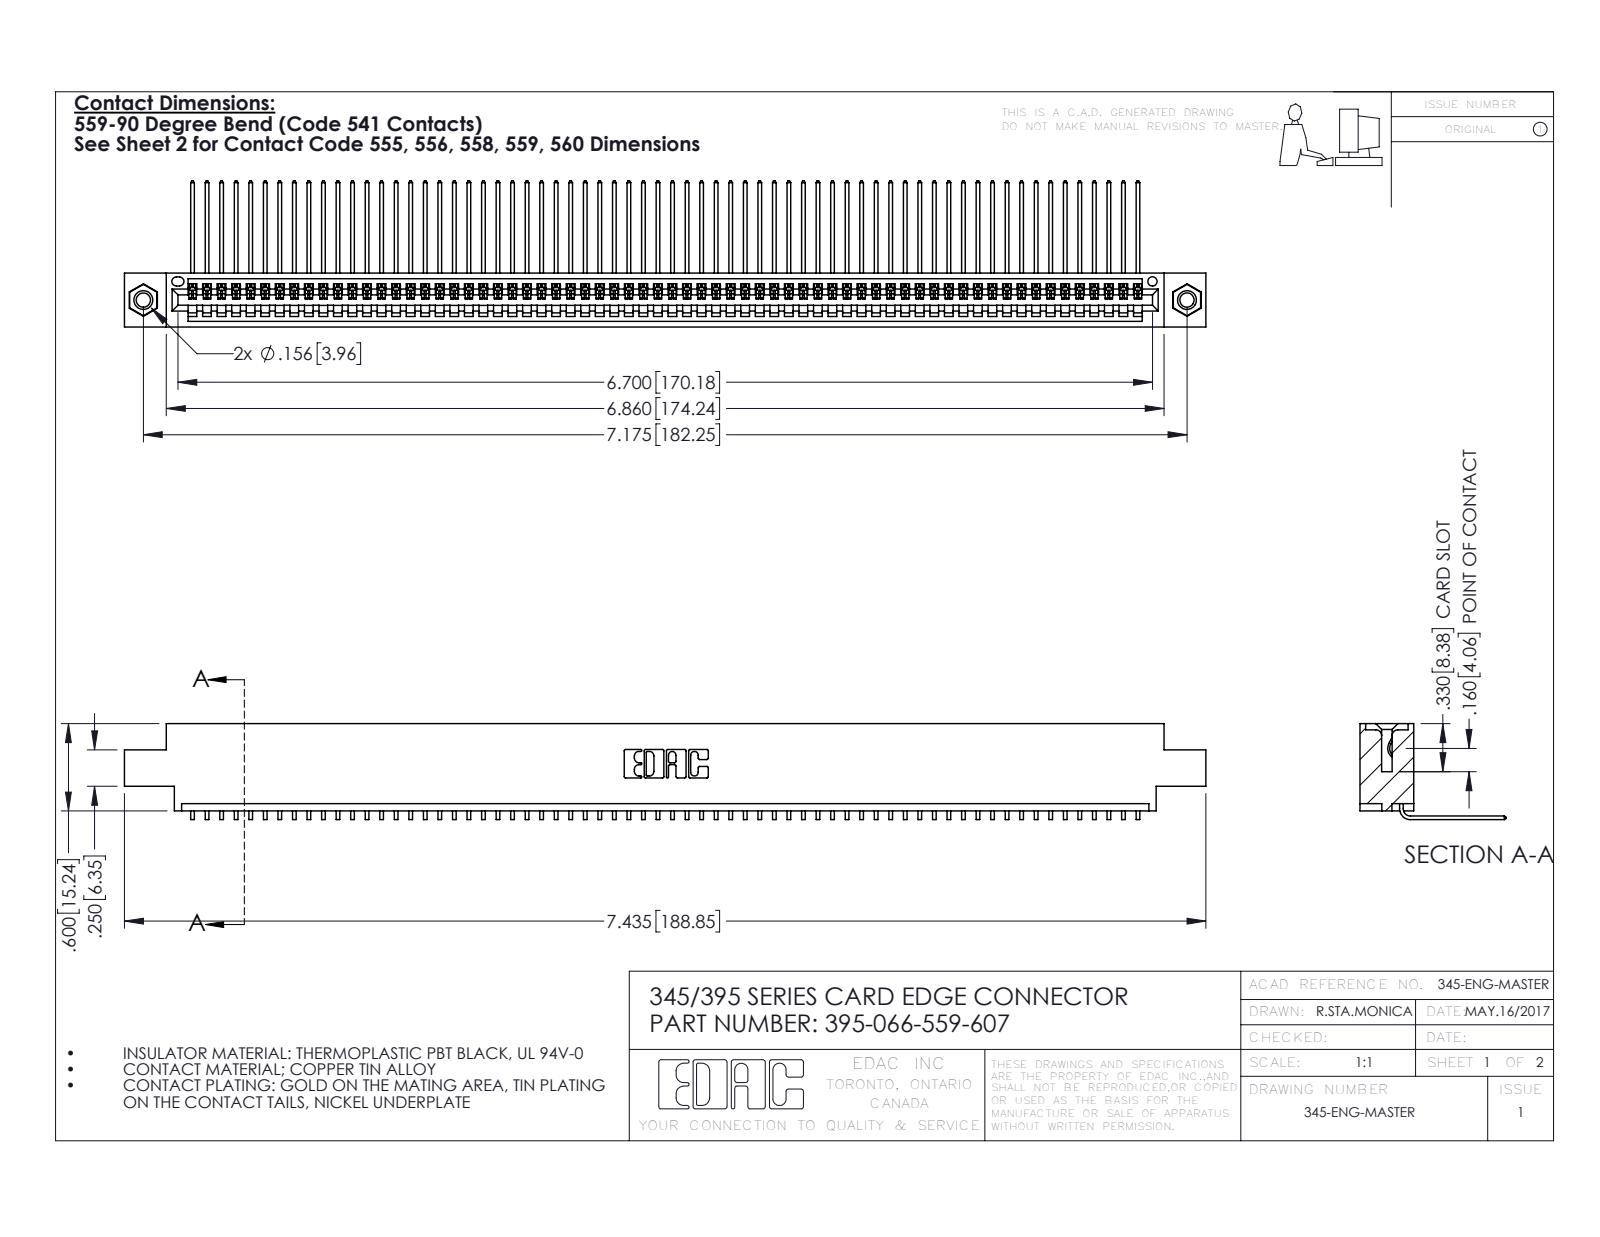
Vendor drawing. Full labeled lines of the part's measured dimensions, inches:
Part name (STEP PRODUCT): 345-292-001_558 559 Tail - 1; 345-250-001_345-250-005-103; 395-066-559-607; 345 Part_0.170 Offset - 0.156 Dia-TI
STEP written by: SolidWorks 2016 (CONFIG_CONTROL_DESIGN)
Units: inches
Bodies: 69 solids, 4150 faces (2888 planar, 1246 cylindrical, 16 other)
Overall size (bounding box): 7.435 × 1.005 × 0.659
Volume: 1.112 in³ · Surface area: 40.3 in²
Round holes (diameter × count): ⌀0.098 ×2, ⌀0.125 ×2, ⌀0.156 ×2, ⌀0.064 ×1
Round bosses / shafts (diameter × count): ⌀0.155 ×2
Partial cylindrical surfaces — rounded edges, fillets, slot ends (radius × count): R0.006 ×132, R0.01 ×22, R0.007 ×6, R0.031 ×6, R0.026 ×3, R0.031 ×2, R0.04 ×2, R0.014 ×1
Main face-to-face distances: 0.072, 0.298, 0.37, 0.2, 0.098, 0.272, 0.025, 0.225, 0.175, 0.149
Hole centre spacings: 0.27, 6.939, 7.175
